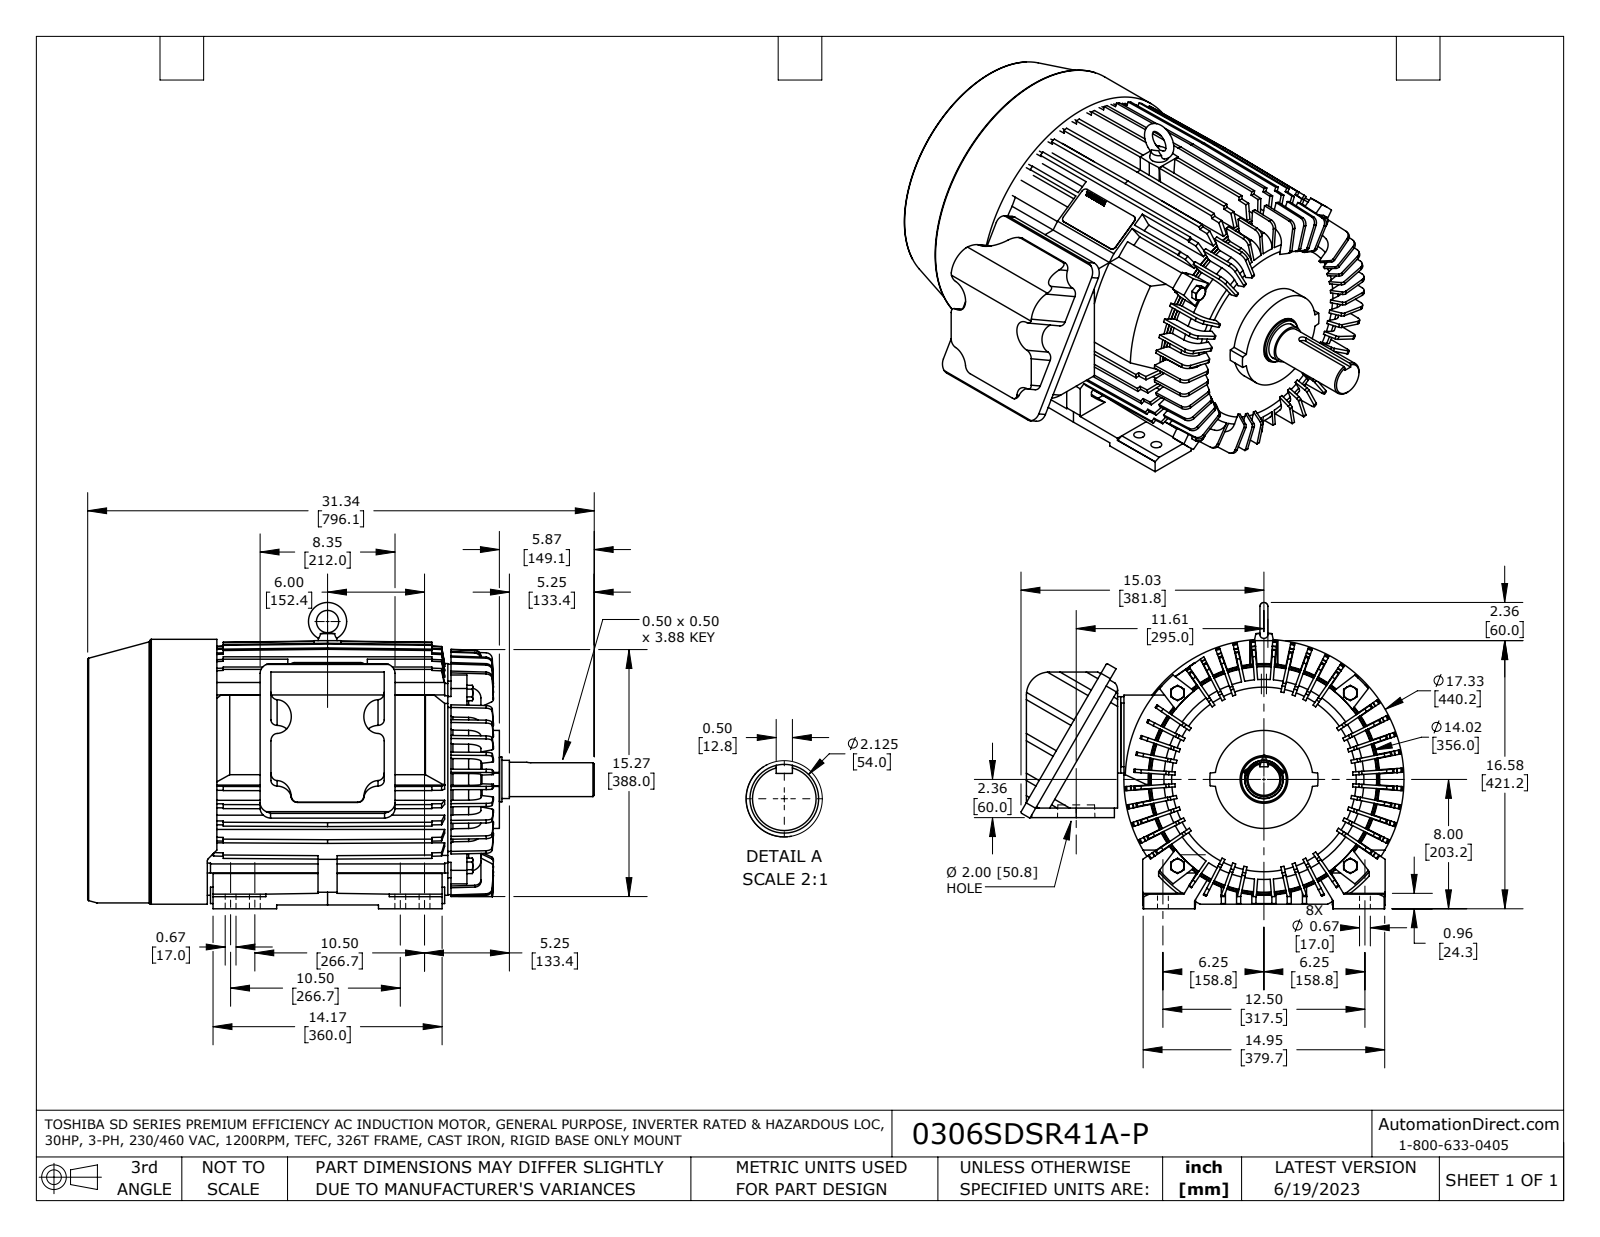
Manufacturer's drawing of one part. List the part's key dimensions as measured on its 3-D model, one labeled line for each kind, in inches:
Part name (STEP PRODUCT): MDSLV001-06-46P-F1-Bottom nc bod broke rep1
STEP written by: SolidWorks 2021 (AUTOMOTIVE_DESIGN)
Units: inches
Bodies: 13 solids, 3440 faces (2627 planar, 248 cylindrical, 565 other)
Overall size (bounding box): 31.343 × 23.696 × 18.945
Volume: 5 445 in³ · Surface area: 4 963 in²
Round holes (diameter × count): ⌀0.354 ×8, ⌀0.669 ×8, ⌀0.087 ×4, ⌀0.398 ×4, ⌀0.551 ×4, ⌀0.472 ×1, ⌀0.545 ×1, ⌀1.26 ×1, ⌀2.382 ×1, ⌀2.756 ×1, ⌀2.953 ×1, ⌀3.937 ×1
Round bosses / shafts (diameter × count): ⌀17.331 ×1, ⌀14.331 ×1, ⌀14.252 ×1, ⌀13.819 ×1, ⌀6.063 ×1, ⌀2.795 ×1, ⌀2.776 ×1, ⌀2.362 ×1
Partial cylindrical surfaces — rounded edges, fillets, slot ends (radius × count): R0.394 ×26, R0.021 ×6, R0.042 ×6, R0.055 ×6, R0.906 ×6, R0.02 ×4, R0.09 ×4, R0.25 ×4
Main face-to-face distances: 0.256, 0.591, 14.882, 14.291, 14.016, 14.606, 0.276, 0.197, 0.256, 7.992
Hole centre spacings: 10.228, 0.669, 1.5, 2.363, 3.341, 6.889, 7.559, 7.702
